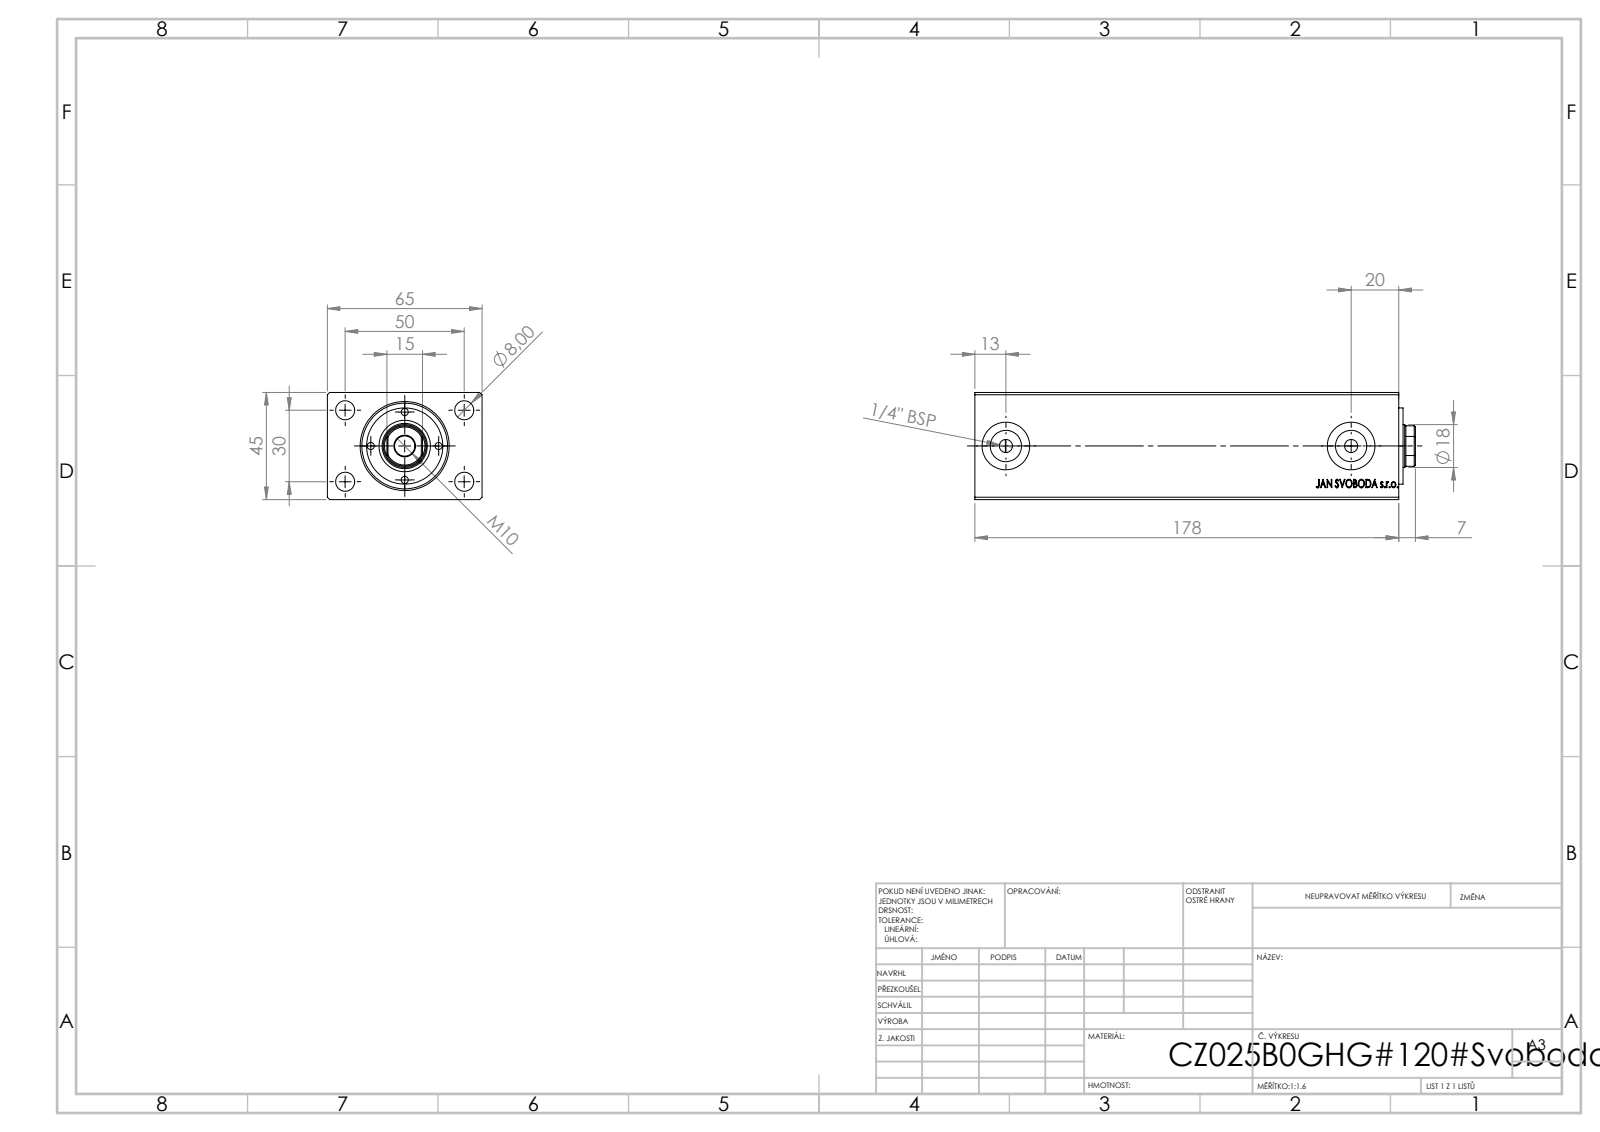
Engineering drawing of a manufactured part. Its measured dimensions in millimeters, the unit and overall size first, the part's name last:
Units: millimetres
Overall size (bounding box): 185 × 65 × 45
Round holes (diameter × count): ⌀3 ×4, ⌀8 ×4, ⌀5.5 ×2, ⌀13.16 ×2, ⌀20 ×2, ⌀8.5 ×1, ⌀18 ×1, ⌀19 ×1, ⌀25 ×1, ⌀36 ×1
Round bosses / shafts (diameter × count): ⌀32 ×1
Partial cylindrical surfaces — rounded edges, fillets, slot ends (radius × count): R8.5 ×1
Main face-to-face distances: 45, 65, 178, 7, 177.8, 165.2, 12.6, 12.8, 1.8, 5.2
Hole centre spacings: 14.25, 18.45, 20.15, 25.01, 29.15, 38.48, 42.02, 28.5
Volume: 477 667 mm³ · Surface area: 78 816 mm²
Bodies: 3 solids, 873 faces (399 planar, 58 cylindrical, 416 other)
Part name (STEP PRODUCT): V500CZ_B_VC; V500CZ
STEP written by: SolidWorks 2019 (CONFIG_CONTROL_DESIGN)
